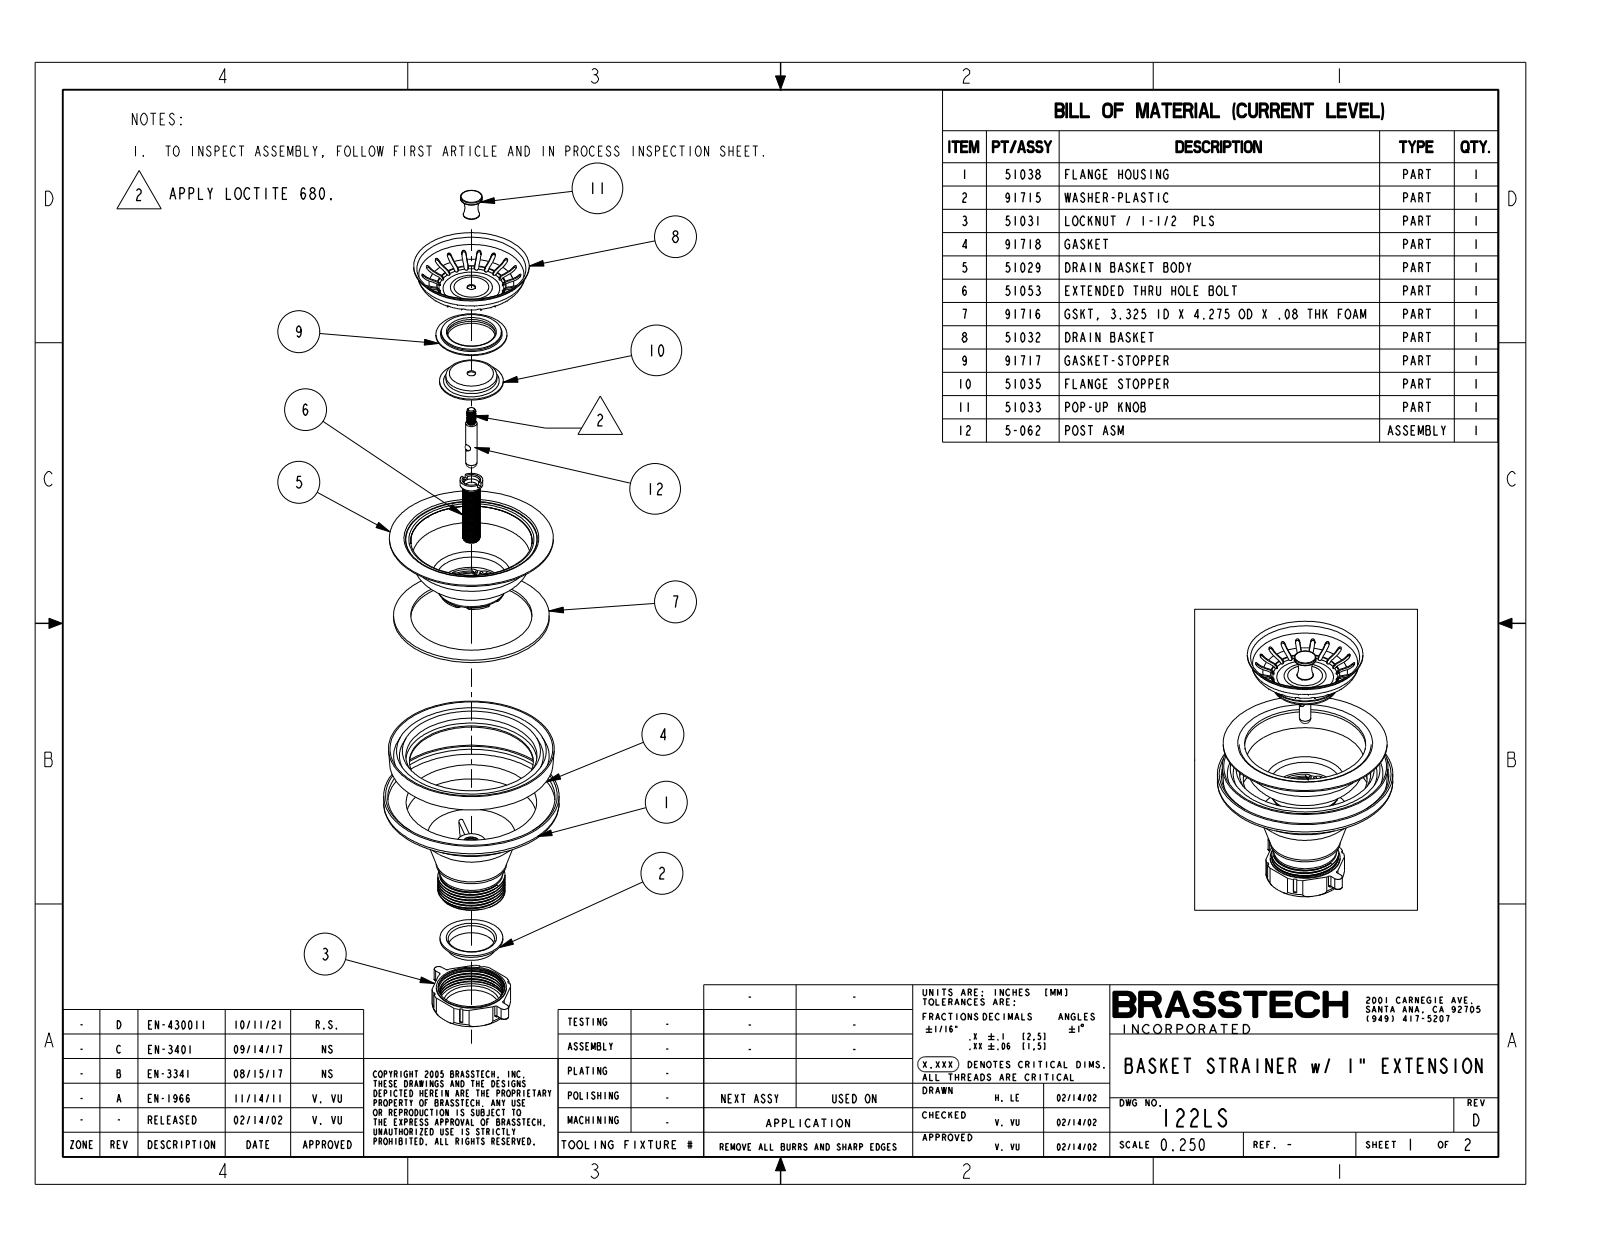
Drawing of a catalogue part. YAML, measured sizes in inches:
part_name: "51038; 91715; 51031; 91718 (+8 more)"
step_written_by: "CREO PARAMETRIC BY PTC INC, 2018400 (AUTOMOTIVE_DESIGN)"
units: inches
bodies: {solids: 15, faces: 1099, planar: 198, cylindrical: 368, other: 533}
overall_size: [7.559, 4.814, 4.814]
volume: 8.766
surface_area: 239.5
round_holes:
  - {diameter: 0.189, count: 1}
  - {diameter: 0.2, count: 1}
  - {diameter: 0.23, count: 1}
  - {diameter: 0.234, count: 1}
  - {diameter: 0.275, count: 1}
  - {diameter: 0.323, count: 1}
  - {diameter: 0.39, count: 1}
  - {diameter: 0.408, count: 1}
  - {diameter: 0.45, count: 1}
  - {diameter: 0.47, count: 1}
  - {diameter: 0.492, count: 1}
  - {diameter: 1.275, count: 1}
round_bosses_or_shafts:
  - {diameter: 4.814, count: 1}
  - {diameter: 4.5, count: 1}
  - {diameter: 4.275, count: 1}
  - {diameter: 3.72, count: 1}
  - {diameter: 3.17, count: 1}
  - {diameter: 1.95, count: 1}
  - {diameter: 1.94, count: 1}
  - {diameter: 1.92, count: 1}
partial_cylinders:
  - {radius: 0.06, count: 40}
  - {radius: 0.073, count: 24}
  - {radius: 0.05, count: 20}
  - {radius: 0.085, count: 16}
  - {radius: 0.02, count: 2}
  - {radius: 0.062, count: 2}
  - {radius: 0.12, count: 2}
  - {radius: 0.853, count: 1}
face_to_face_distances: [1.224, 0.08, 0.035, 1.144, 1.259, 0.115, 0.151, 1.295, 1.375, 1.41]
